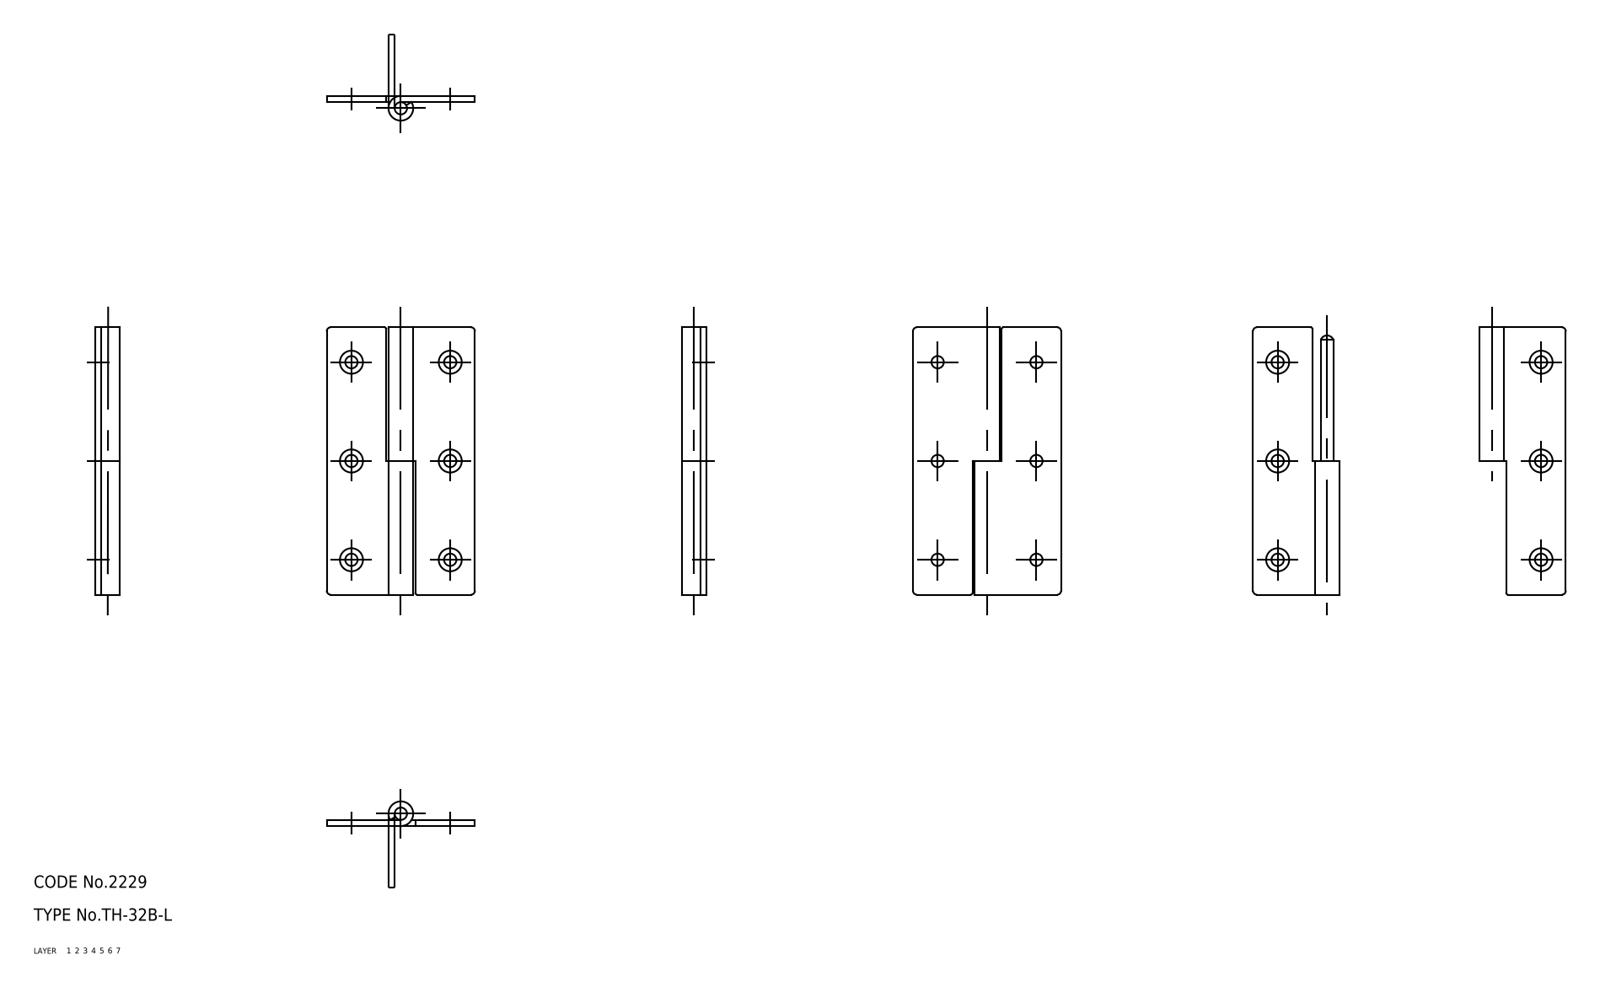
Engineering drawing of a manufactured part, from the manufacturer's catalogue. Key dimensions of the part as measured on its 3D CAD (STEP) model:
Part name (STEP PRODUCT): shaft; hinge piece_B; hinge piece_A; TH_32B_L_7746_36
STEP written by: CADfix (AUTOMOTIVE_DESIGN)
Units: millimetres
Bodies: 3 solids, 54 faces (0 planar, 0 cylindrical, 54 other)
Overall size (bounding box): 65 × 36 × 6
Volume: 4 630 mm³ · Surface area: 6 887 mm²
